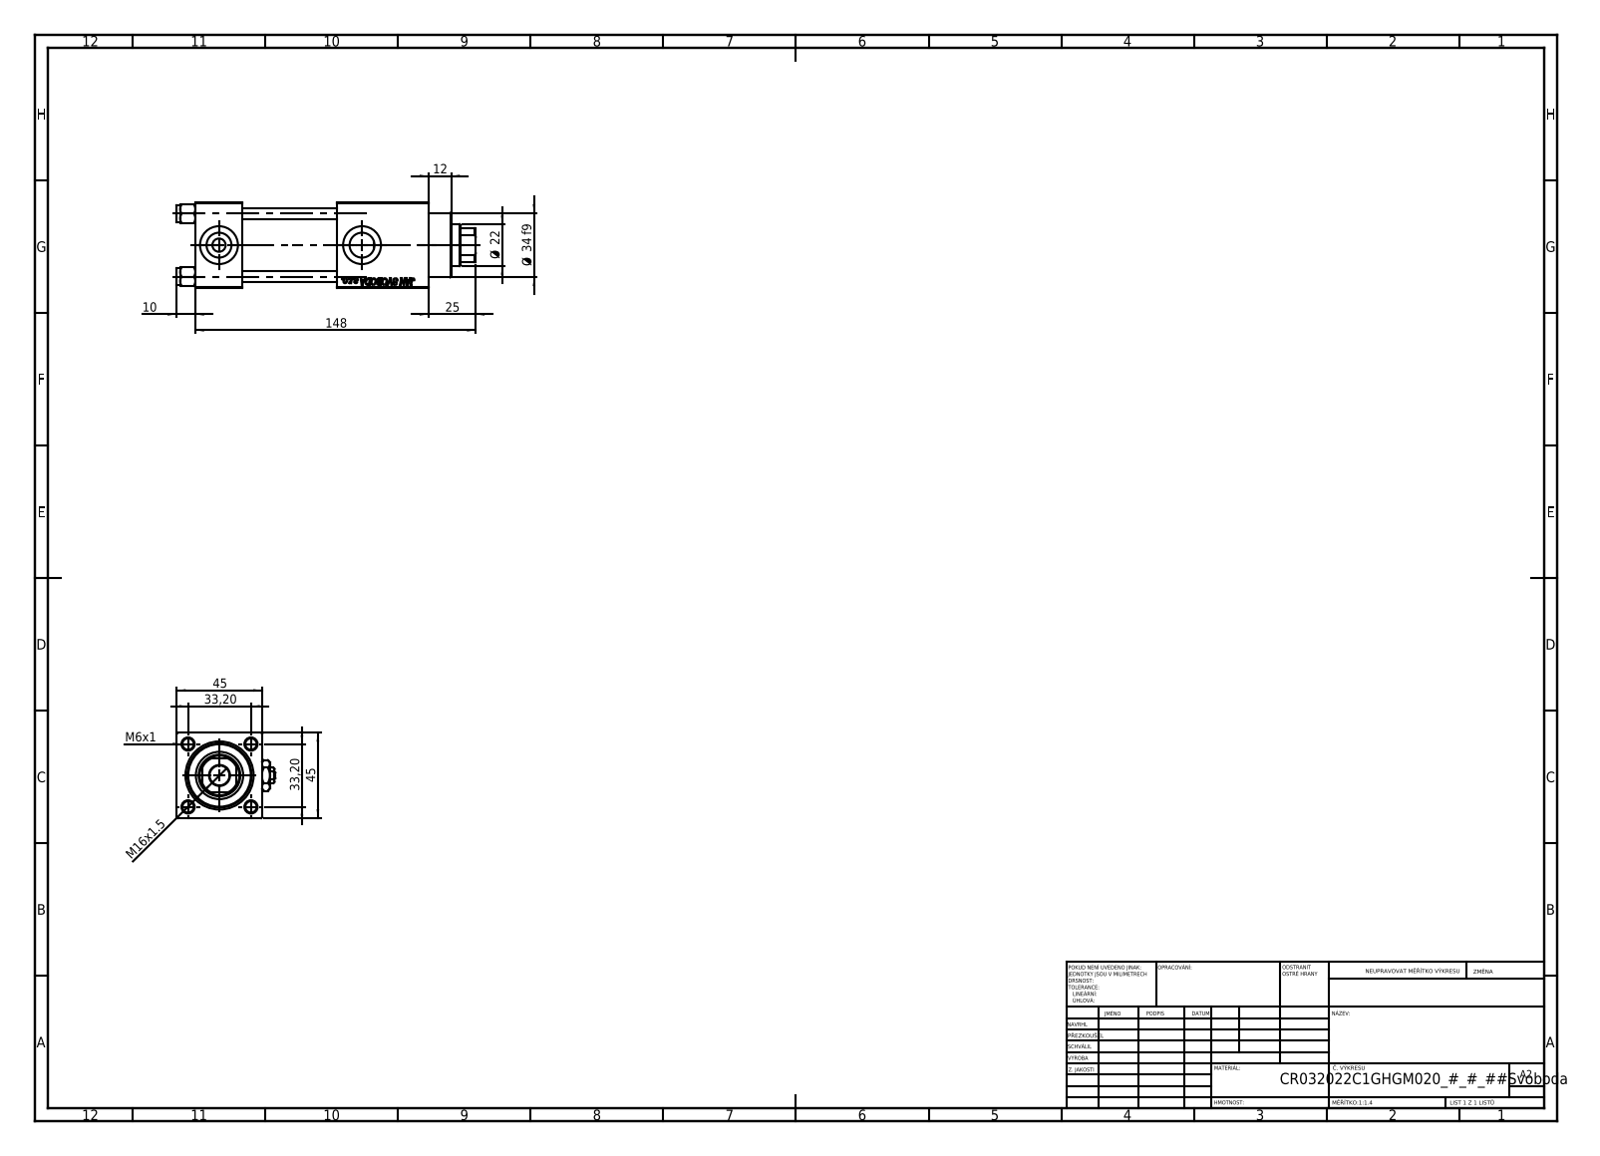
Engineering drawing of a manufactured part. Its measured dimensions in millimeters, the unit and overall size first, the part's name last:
Units: millimetres
Overall size (bounding box): 158 × 52 × 45
Round holes (diameter × count): ⌀6 ×4, ⌀7 ×2, ⌀13.16 ×2, ⌀20 ×2, ⌀10.5 ×1, ⌀22 ×1, ⌀24 ×1, ⌀25 ×1, ⌀32 ×1, ⌀33 ×1
Round bosses / shafts (diameter × count): ⌀9 ×4, ⌀38 ×1, ⌀34 ×1
Partial cylindrical surfaces — rounded edges, fillets, slot ends (radius × count): R10.5 ×1
Main face-to-face distances: 45, 25, 50, 123, 75, 98, 48, 94.3, 69.3, 19.3
Hole centre spacings: 23.48, 33.2, 46.95, 75.5
Volume: 209 155 mm³ · Surface area: 72 064 mm²
Bodies: 12 solids, 1195 faces (549 planar, 90 cylindrical, 556 other)
Part name (STEP PRODUCT): V215_VC_A; V215CR_C_TYCINKA; Zatka_pro_OIL_PORT; V215CR_C_Body (+2 more)
STEP written by: SolidWorks 2019 (CONFIG_CONTROL_DESIGN)
